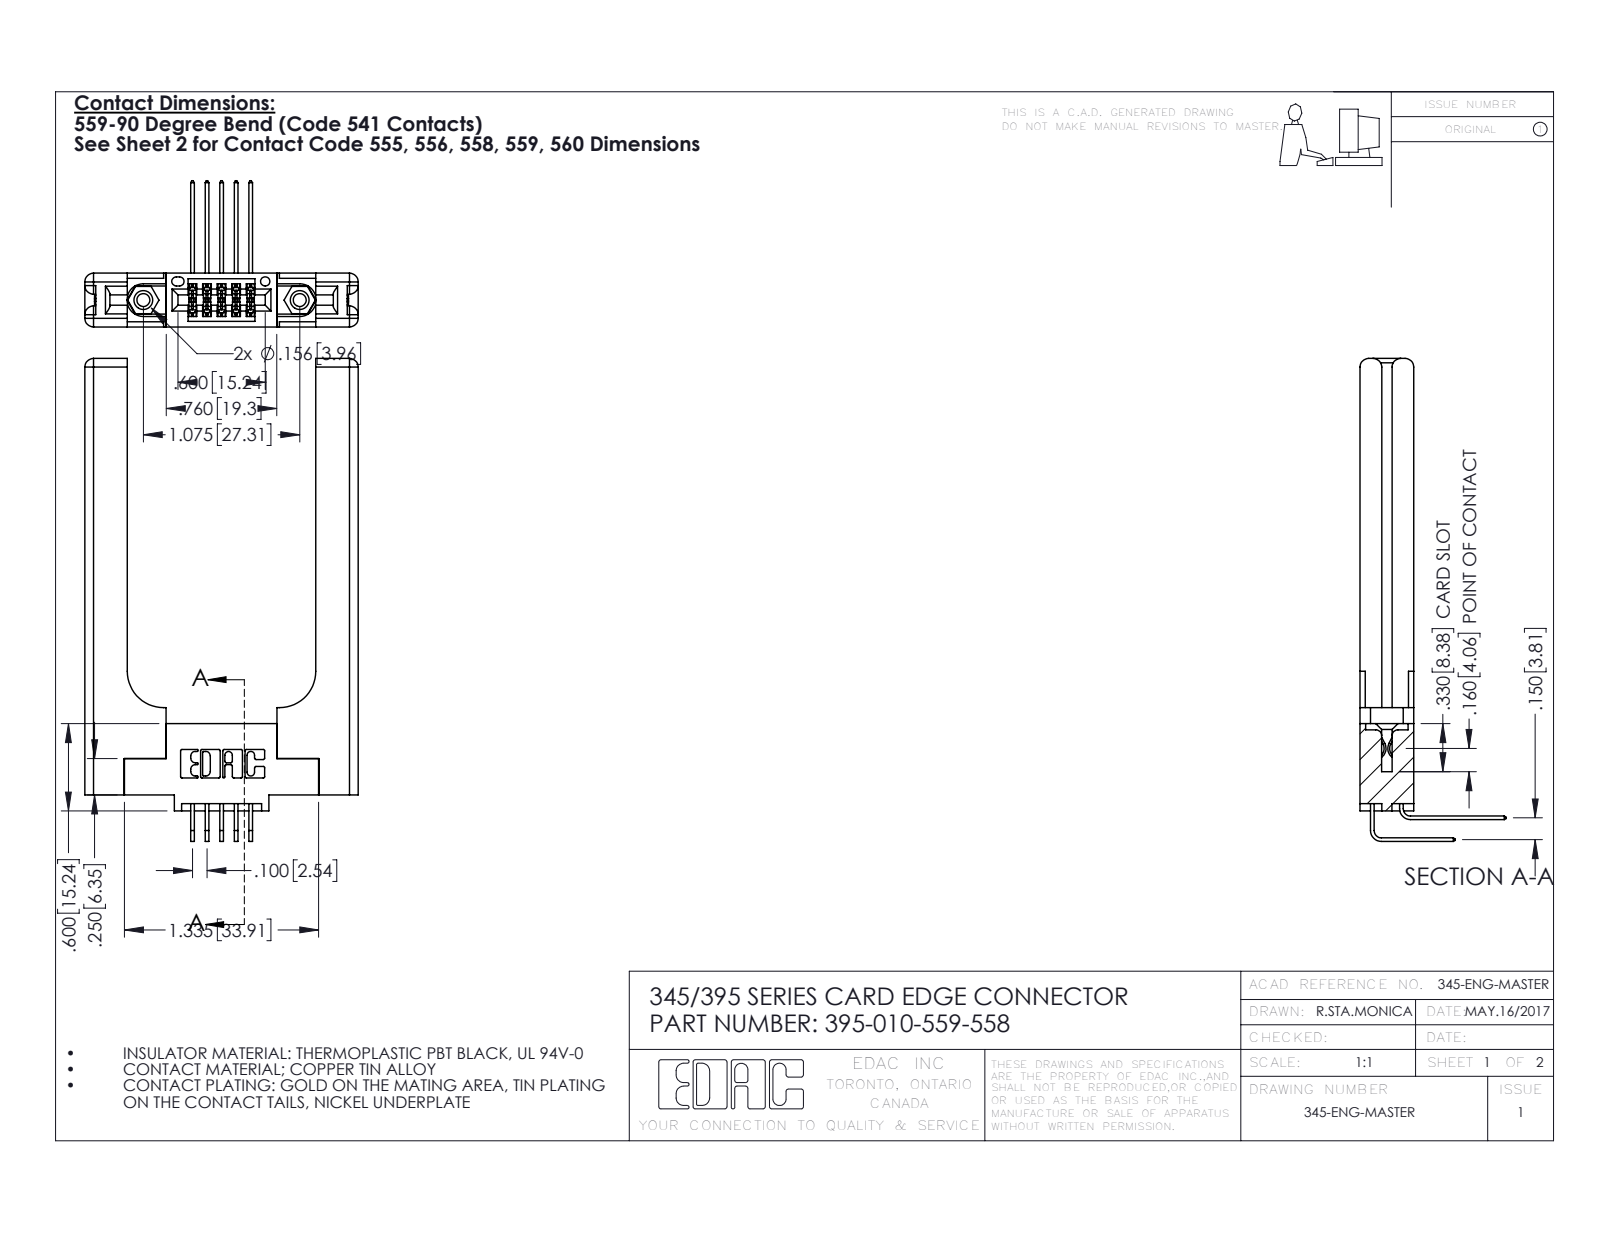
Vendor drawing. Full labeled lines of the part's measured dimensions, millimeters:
Part name (STEP PRODUCT): 345-292-001_558 559 Tail - 1; 345-250-001_345-250-001-102; 395-010-559-558; 345-220-058_345-220-058 (+2 more)
STEP written by: SolidWorks 2016 (CONFIG_CONTROL_DESIGN)
Units: millimetres
Bodies: 15 solids, 906 faces (582 planar, 264 cylindrical, 60 other)
Overall size (bounding box): 84.3 × 47.7 × 25.5
Volume: 12 700 mm³ · Surface area: 11 030 mm²
Round holes (diameter × count): ⌀2.3 ×2, ⌀3.2 ×2, ⌀4 ×2, ⌀1.6 ×1
Round bosses / shafts (diameter × count): ⌀3.9 ×2
Partial cylindrical surfaces — rounded edges, fillets, slot ends (radius × count): R0.3 ×22, R0.2 ×16, R1.5 ×16, R0.2 ×6, R0.8 ×6, R0.7 ×3, R0.4 ×2, R0.5 ×2
Main face-to-face distances: 9.4, 3.8, 5.6, 1.8, 32.9, 3.8, 2, 7.6, 1.8, 7.4
Hole centre spacings: 6.9, 21.5, 27.3
